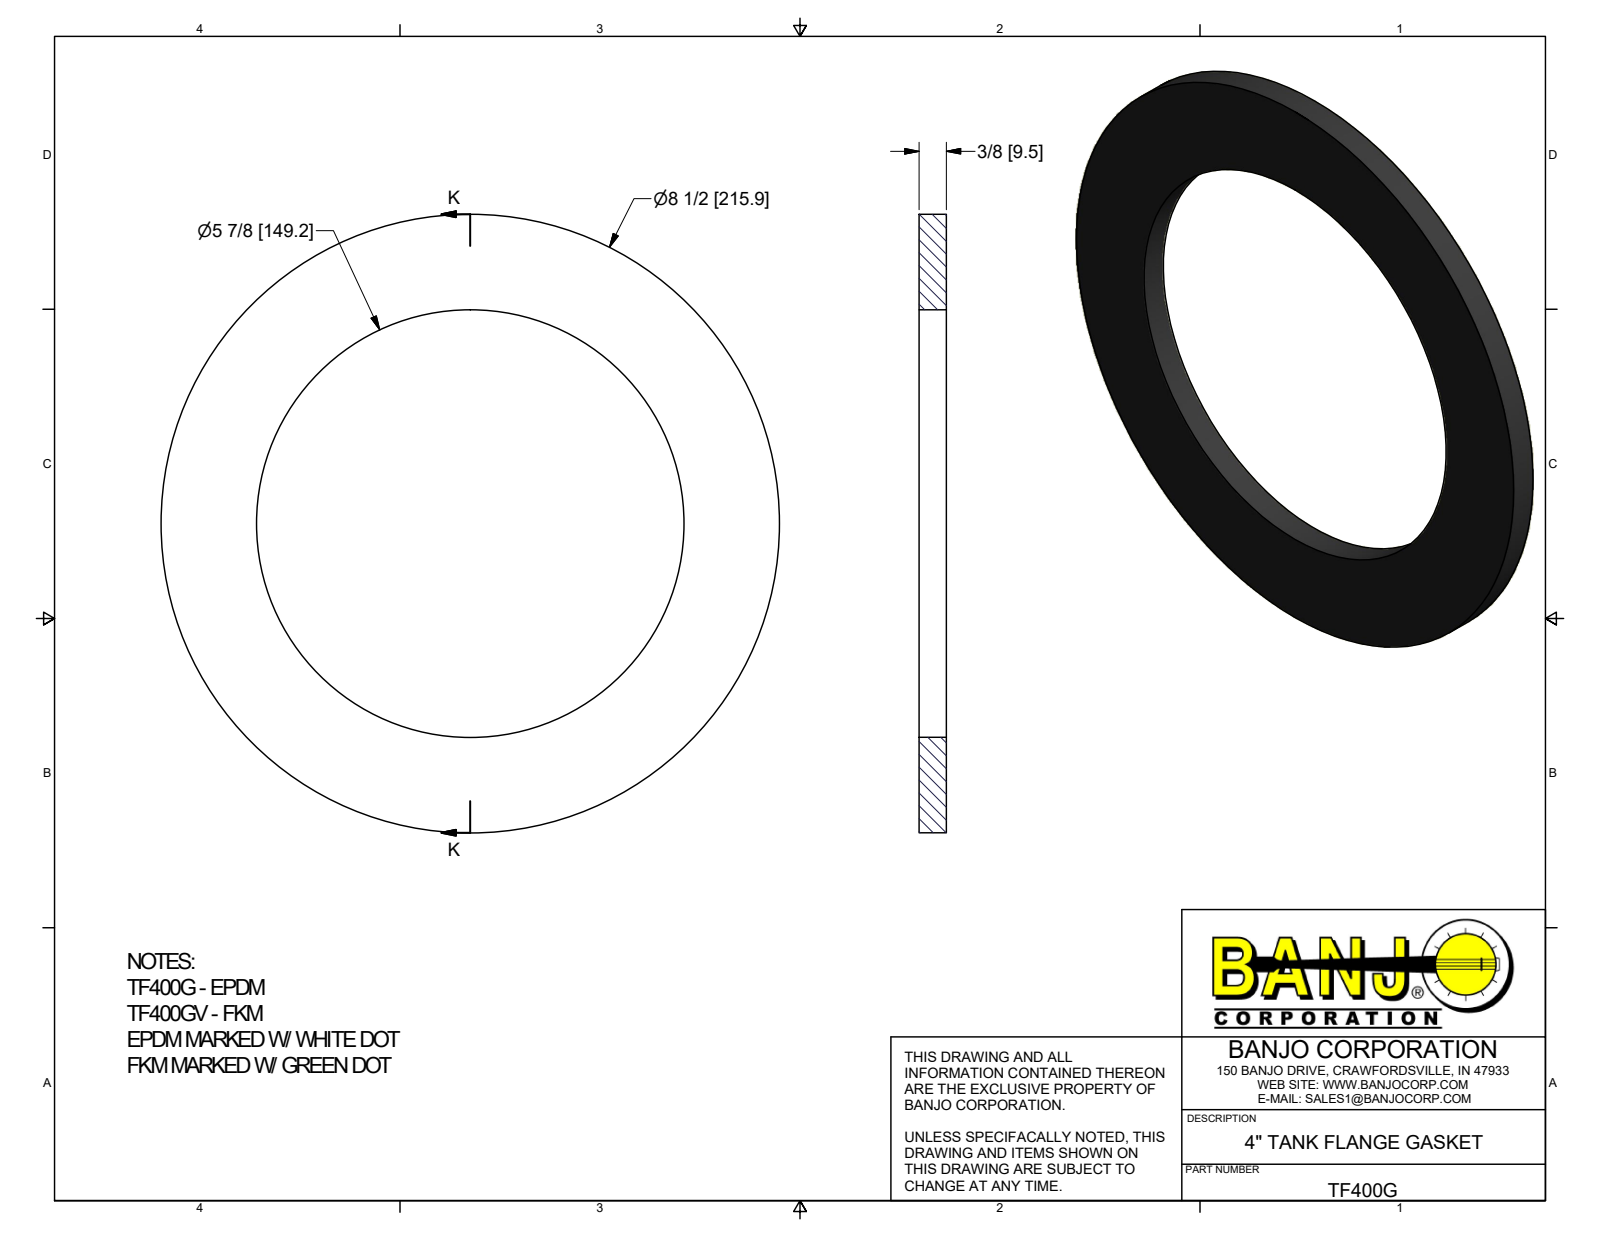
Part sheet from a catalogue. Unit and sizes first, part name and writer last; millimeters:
Units: millimetres
Overall size (bounding box): 215.9 × 215.9 × 9.53
Round holes (diameter × count): ⌀149.22 ×1
Round bosses / shafts (diameter × count): ⌀215.9 ×1
Main face-to-face distances: 9.52
Volume: 182 121 mm³ · Surface area: 49 166 mm²
Bodies: 1 solid, 4 faces (2 planar, 2 cylindrical, 0 other)
Part name (STEP PRODUCT): TF400G
STEP written by: Autodesk Inventor 2017 (AUTOMOTIVE_DESIGN)
